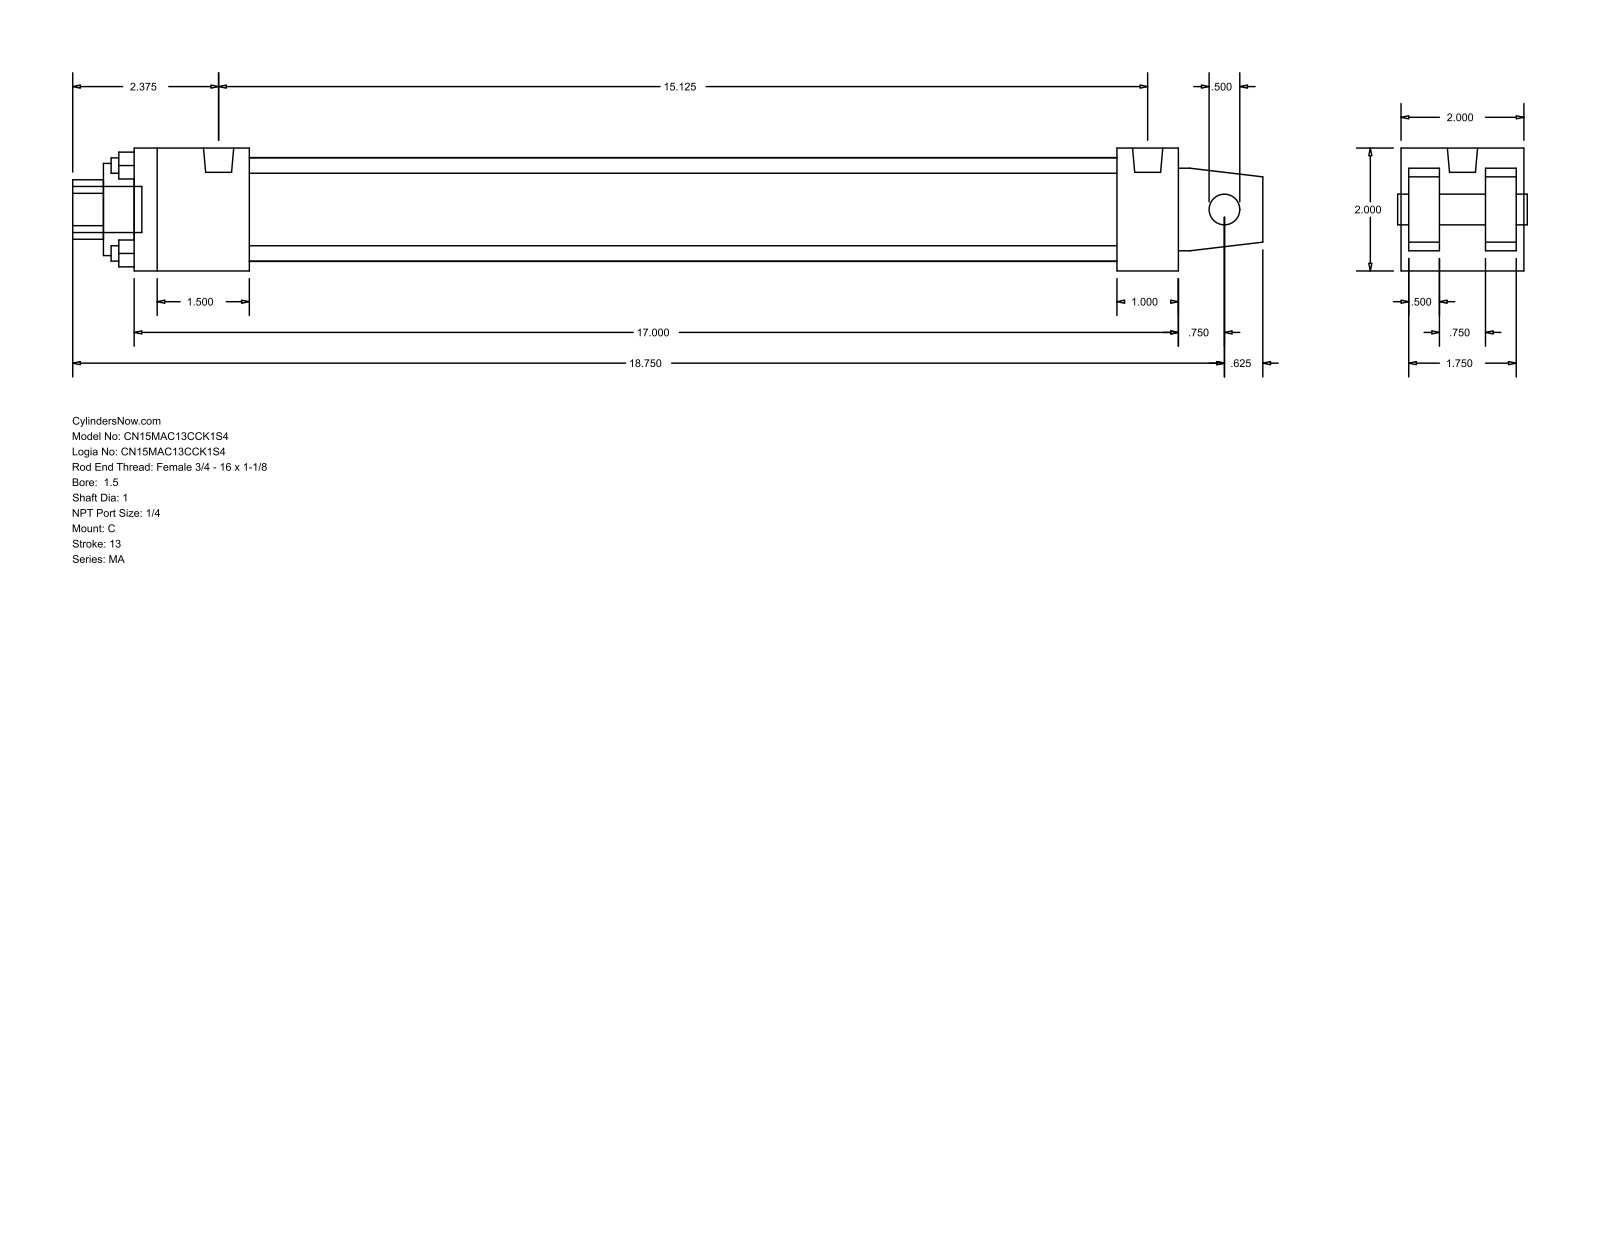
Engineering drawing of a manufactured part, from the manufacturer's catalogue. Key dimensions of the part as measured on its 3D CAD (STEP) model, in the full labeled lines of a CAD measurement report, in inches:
Part name (STEP PRODUCT): MA_C__0150_1
STEP written by: GSSL Pune (CONFIG_CONTROL_DESIGN)
Units: inches
Bodies: 0 solids, 103 faces (76 planar, 27 cylindrical, 0 other)
Overall size (bounding box): 19.375 × 2 × 2
Round holes (diameter × count): ⌀0.25 ×4, ⌀0.5 ×1, ⌀1 ×1, ⌀1.5 ×1, ⌀1.69 ×1
Round bosses / shafts (diameter × count): ⌀0.313 ×4, ⌀0.492 ×2, ⌀0.75 ×1
Partial cylindrical surfaces — rounded edges, fillets, slot ends (radius × count): R0.484 ×1
Main face-to-face distances: 2, 1.875, 0.5, 0.125, 0.625, 1.375, 1.25, 1.75, 17, 1
Hole centre spacings: 1.011, 1.43, 2.022
